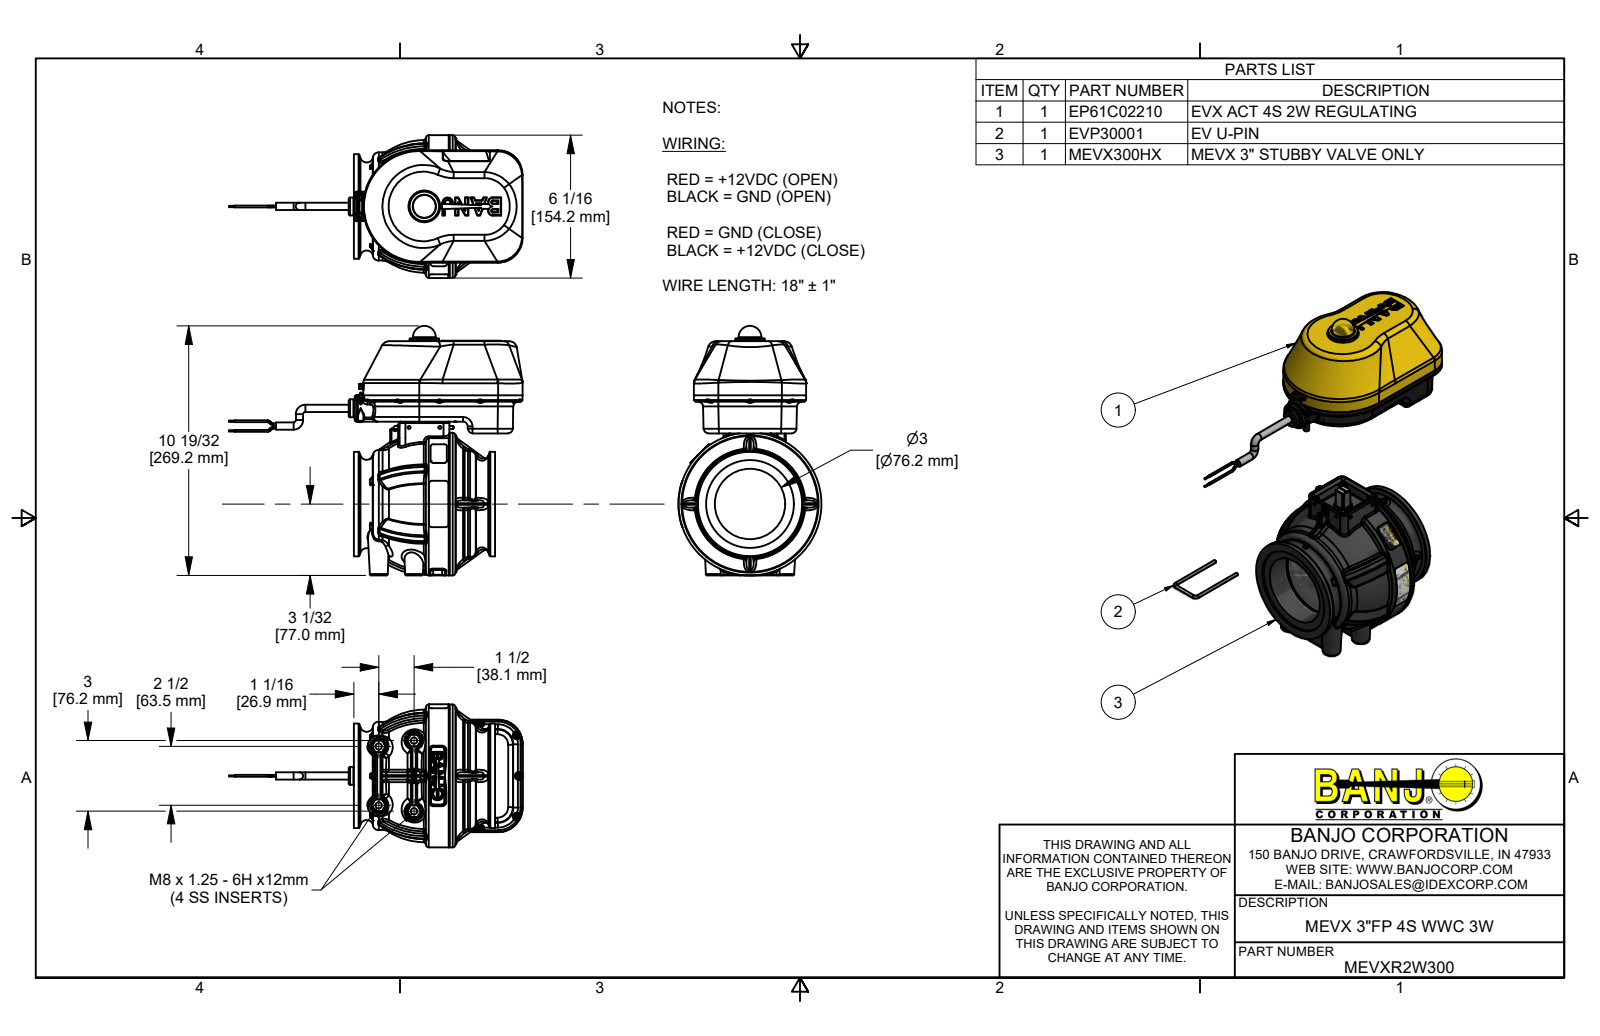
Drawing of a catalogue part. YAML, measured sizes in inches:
part_name: "MEVXR2W300; MEVX300HX; MEVPS30254H; MEVPS30254HX (+8 more)"
step_written_by: "Autodesk Inventor 2019 (AUTOMOTIVE_DESIGN)"
units: inches
bodies: {solids: 80, faces: 9575, planar: 3664, cylindrical: 3118, other: 2793}
overall_size: [12.476, 10.6, 6.072]
volume: 89.57
surface_area: 889.8
round_holes:
  - {diameter: 0.095, count: 11}
  - {diameter: 0.15, count: 11}
  - {diameter: 0.34, count: 11}
  - {diameter: 0.135, count: 6}
  - {diameter: 0.104, count: 4}
  - {diameter: 0.115, count: 4}
  - {diameter: 0.136, count: 4}
  - {diameter: 0.176, count: 4}
  - {diameter: 0.262, count: 4}
  - {diameter: 0.266, count: 4}
  - {diameter: 0.433, count: 4}
  - {diameter: 0.089, count: 2}
round_bosses_or_shafts:
  - {diameter: 0.25, count: 19}
  - {diameter: 0.14, count: 11}
  - {diameter: 0.108, count: 11}
  - {diameter: 0.085, count: 11}
  - {diameter: 0.08, count: 10}
  - {diameter: 0.437, count: 4}
  - {diameter: 0.375, count: 4}
  - {diameter: 0.219, count: 4}
partial_cylinders:
  - {radius: 0.405, count: 138}
  - {radius: 0.387, count: 114}
  - {radius: 0.309, count: 112}
  - {radius: 0.253, count: 108}
  - {radius: 0.609, count: 106}
  - {radius: 0.01, count: 68}
  - {radius: 0.04, count: 46}
  - {radius: 0.05, count: 43}
face_to_face_distances: [0.083, 0.5, 0.085, 0.096, 0.181, 2.175, 2.356, 2.271, 0.125, 0.1]
hole_center_spacings: [3.316, 1.313, 1.563, 1.69, 2.315, 0.523, 0.55, 0.646]
